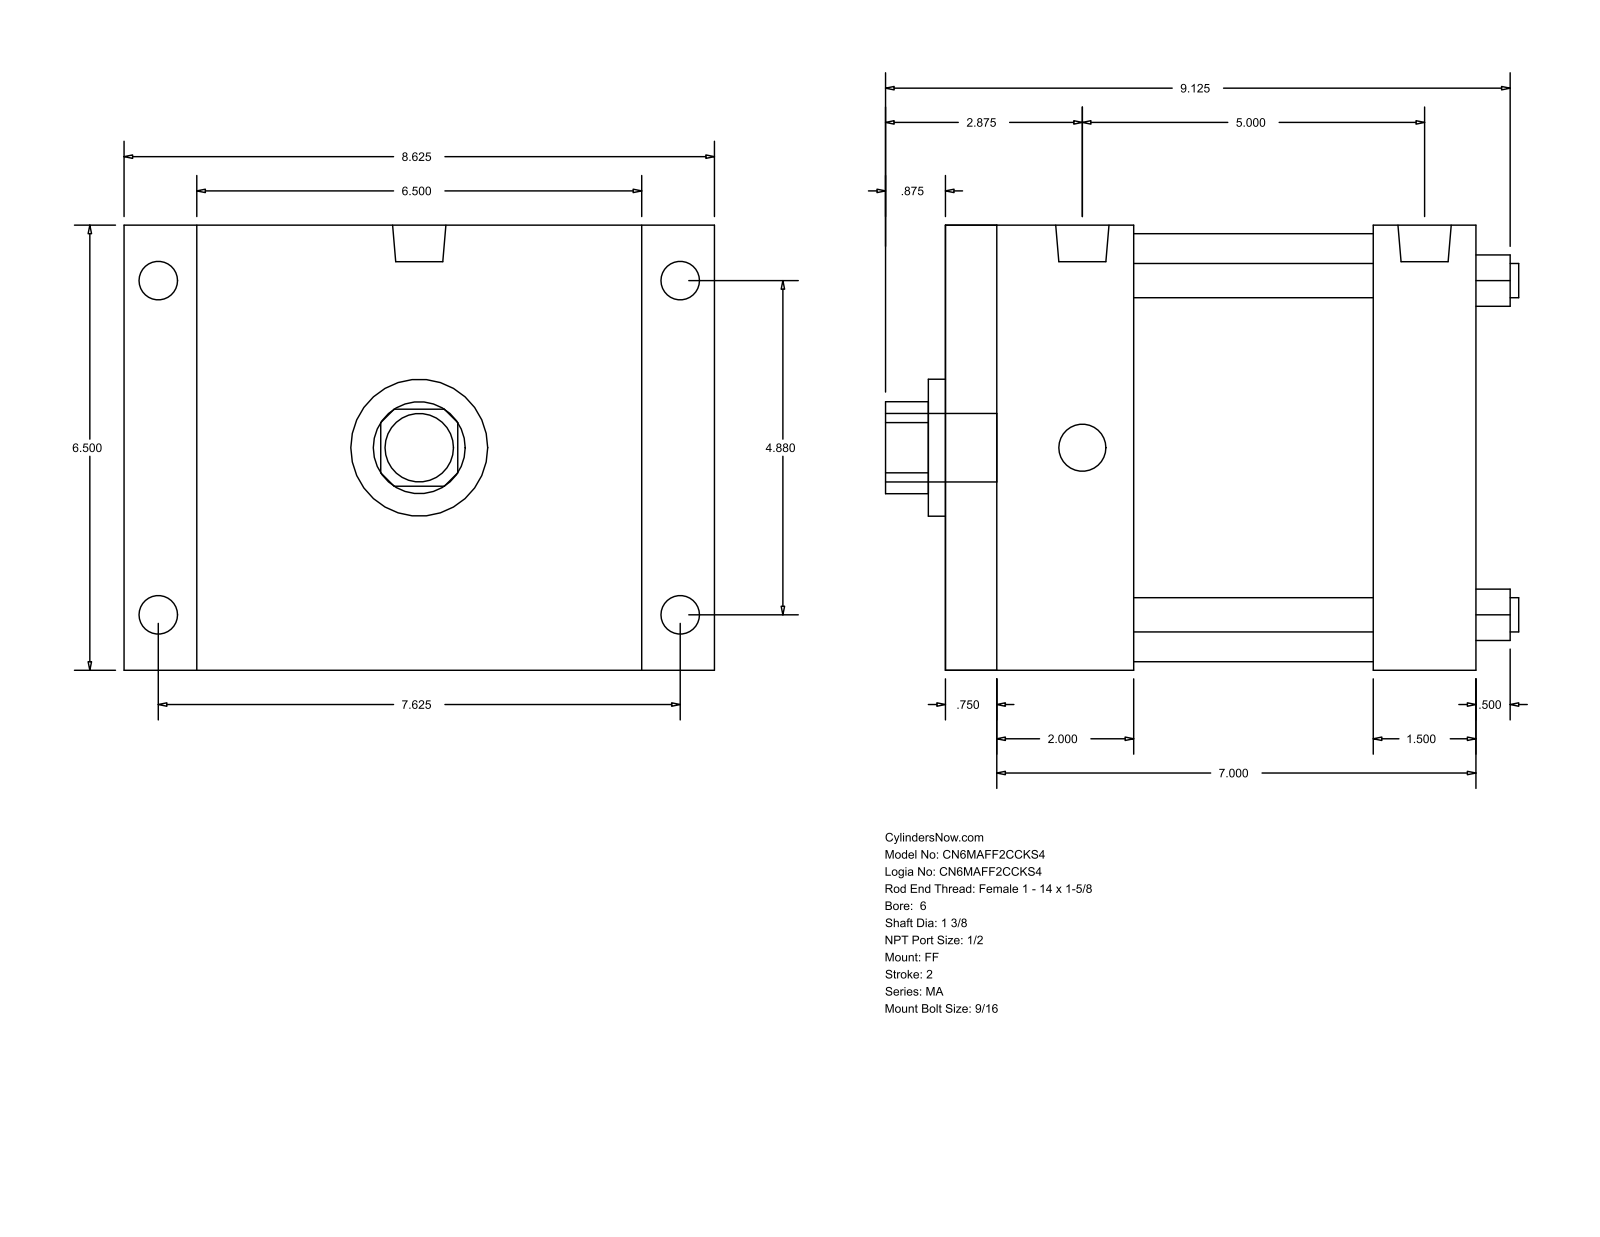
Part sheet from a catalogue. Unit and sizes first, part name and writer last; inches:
Units: inches
Overall size (bounding box): 9.25 × 8.625 × 6.5
Round holes (diameter × count): ⌀0.5 ×4, ⌀1.375 ×1, ⌀2 ×1, ⌀6.25 ×1
Round bosses / shafts (diameter × count): ⌀0.687 ×4, ⌀0.563 ×4, ⌀0.778 ×2, ⌀1 ×1
Partial cylindrical surfaces — rounded edges, fillets, slot ends (radius × count): R0.672 ×1
Main face-to-face distances: 6.5, 7.75, 7.125, 0.625, 1.5, 2.625, 2, 5.125, 6.25, 5.625
Hole centre spacings: 3.451, 4.88, 6.902
Bodies: 0 solids, 92 faces (64 planar, 28 cylindrical, 0 other)
Part name (STEP PRODUCT): MA_FF__0600_1.375
STEP written by: GSSL Pune (CONFIG_CONTROL_DESIGN)
